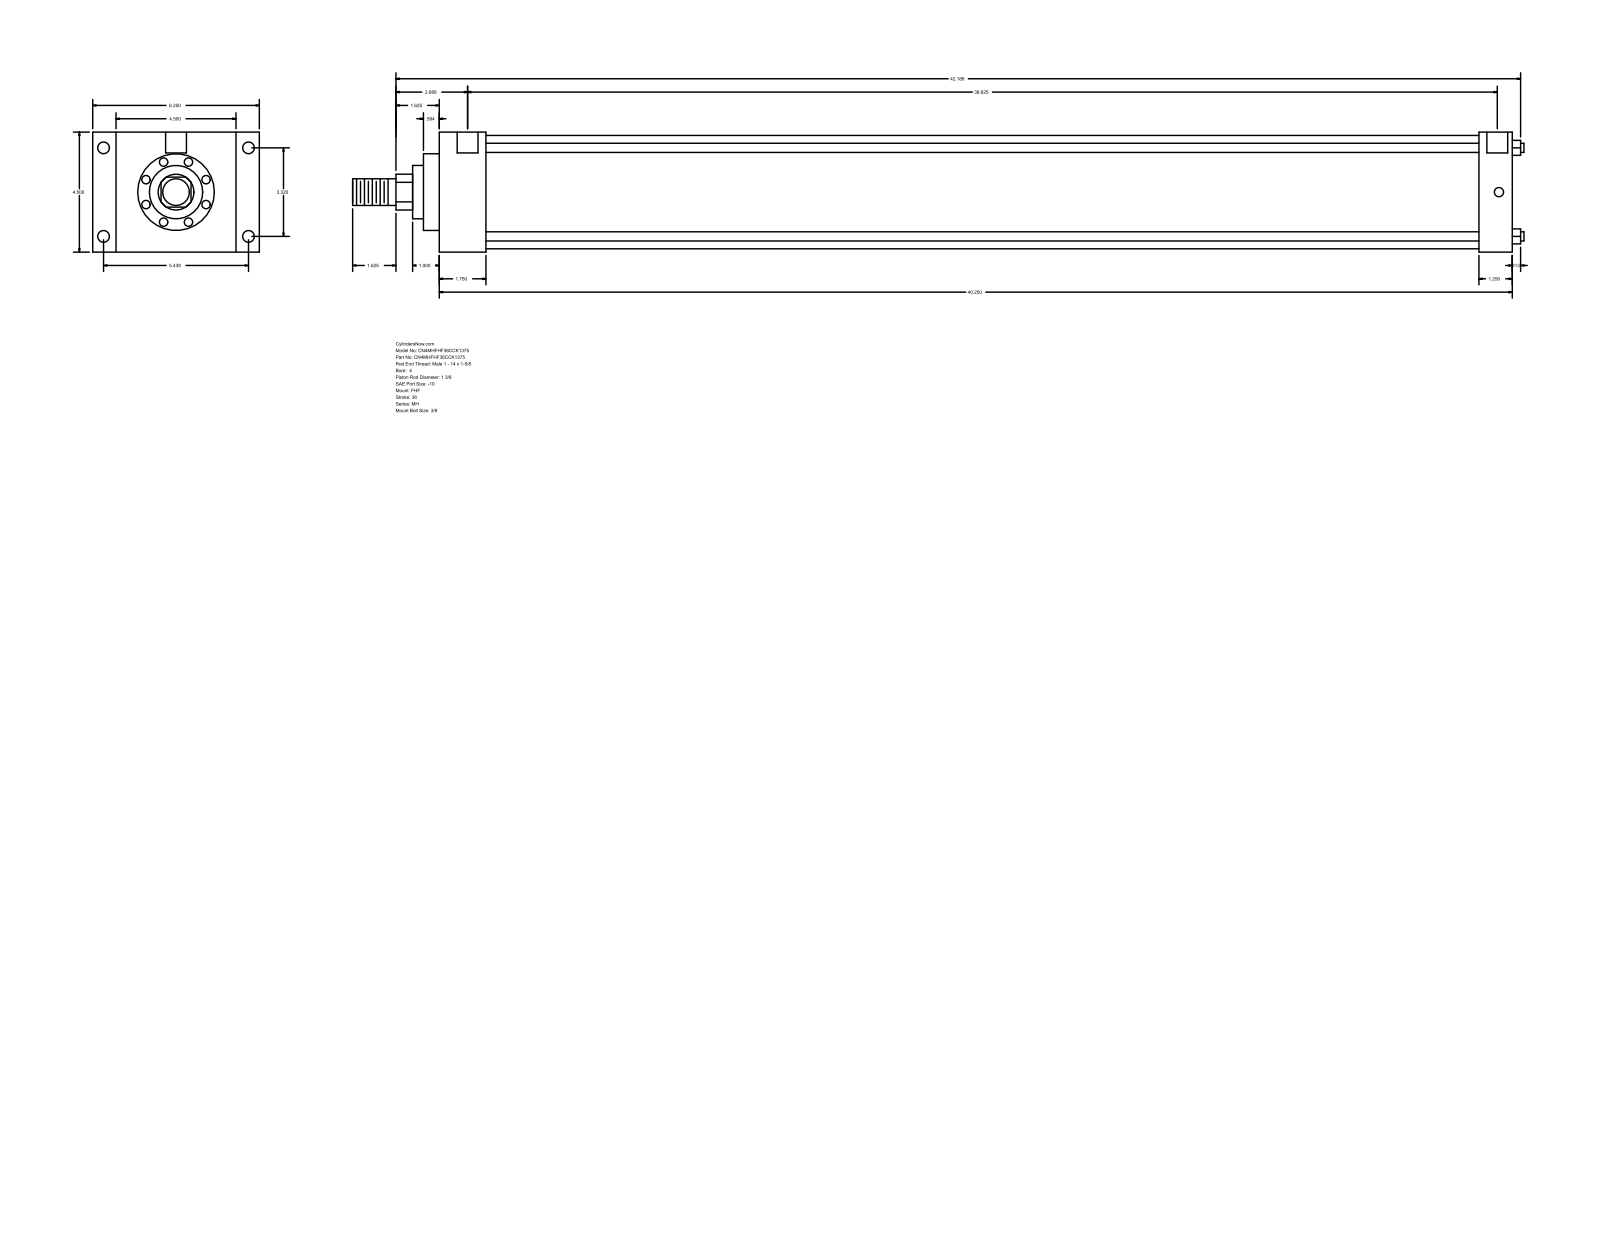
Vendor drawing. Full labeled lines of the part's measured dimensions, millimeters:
Part name (STEP PRODUCT): MH_FHF__0400_1.375
STEP written by: GSSL Pune (CONFIG_CONTROL_DESIGN)
Units: millimetres
Bodies: 0 solids, 90 faces (61 planar, 29 cylindrical, 0 other)
Overall size (bounding box): 1116.01 × 158.75 × 114.3
Round holes (diameter × count): ⌀8.73 ×4, ⌀11.13 ×4, ⌀19.84 ×2
Round bosses / shafts (diameter × count): ⌀8.76 ×4, ⌀107.95 ×1, ⌀73.03 ×1, ⌀50.8 ×1, ⌀34.92 ×1, ⌀25.4 ×1
Partial cylindrical surfaces — rounded edges, fillets, slot ends (radius × count): R17.06 ×1
Main face-to-face distances: 114.3, 1022.35, 44.45, 977.9, 22.23, 136.53, 158.76, 990.61, 946.16, 31.74
Hole centre spacings: 84.32, 138.12, 161.82, 984.25, 1.58, 1.59, 981.08, 982.66
